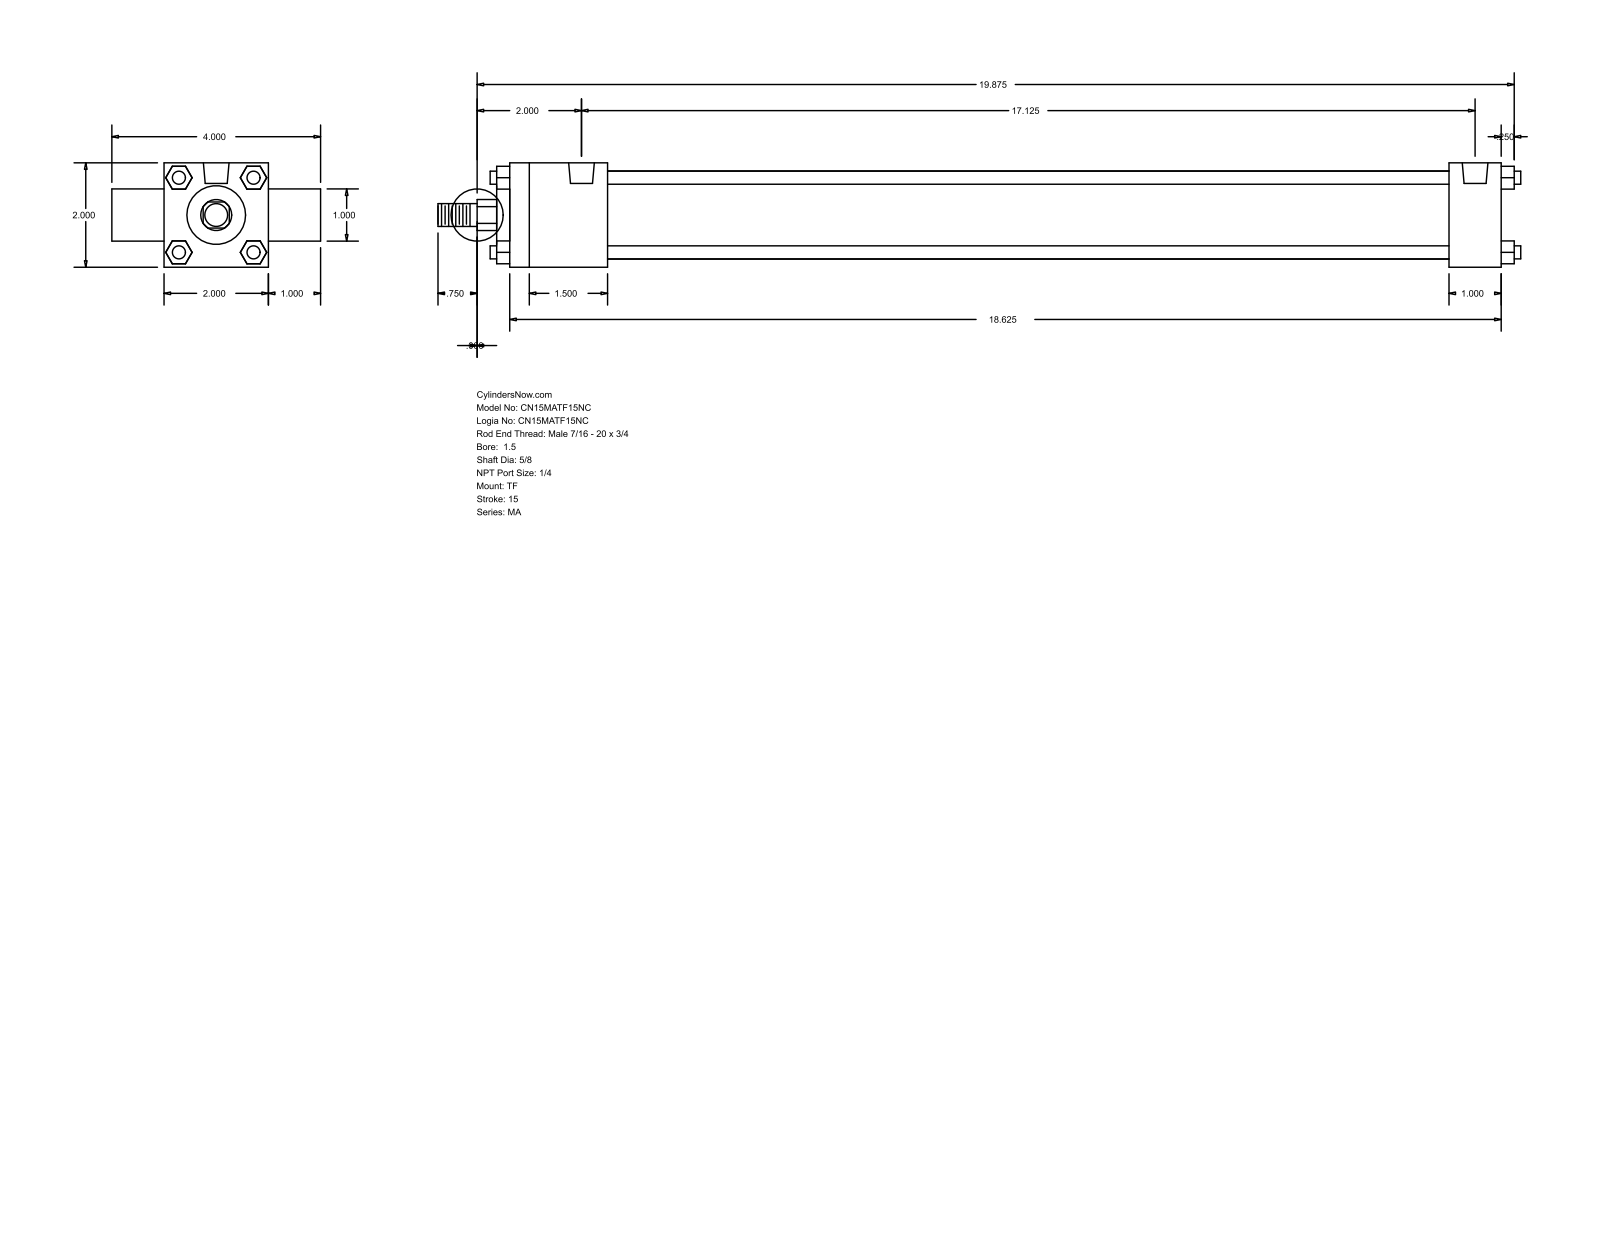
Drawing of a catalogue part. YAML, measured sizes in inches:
part_name: "MA_TF__0150_0.625"
step_written_by: "GSSL Pune (CONFIG_CONTROL_DESIGN)"
units: inches
bodies: {solids: 0, faces: 120, planar: 92, cylindrical: 28, other: 0}
overall_size: [20.75, 4, 2]
round_holes:
  - {diameter: 0.313, count: 3}
  - {diameter: 0.492, count: 2}
round_bosses_or_shafts:
  - {diameter: 0.25, count: 4}
  - {diameter: 1.69, count: 1}
  - {diameter: 1.125, count: 1}
  - {diameter: 1, count: 1}
  - {diameter: 0.625, count: 1}
  - {diameter: 0.437, count: 1}
partial_cylinders:
  - {radius: 0.297, count: 1}
face_to_face_distances: [2, 19, 1, 3, 1.875, 18, 16.125, 17.125, 1, 0.25]
hole_center_spacings: [17.125]
